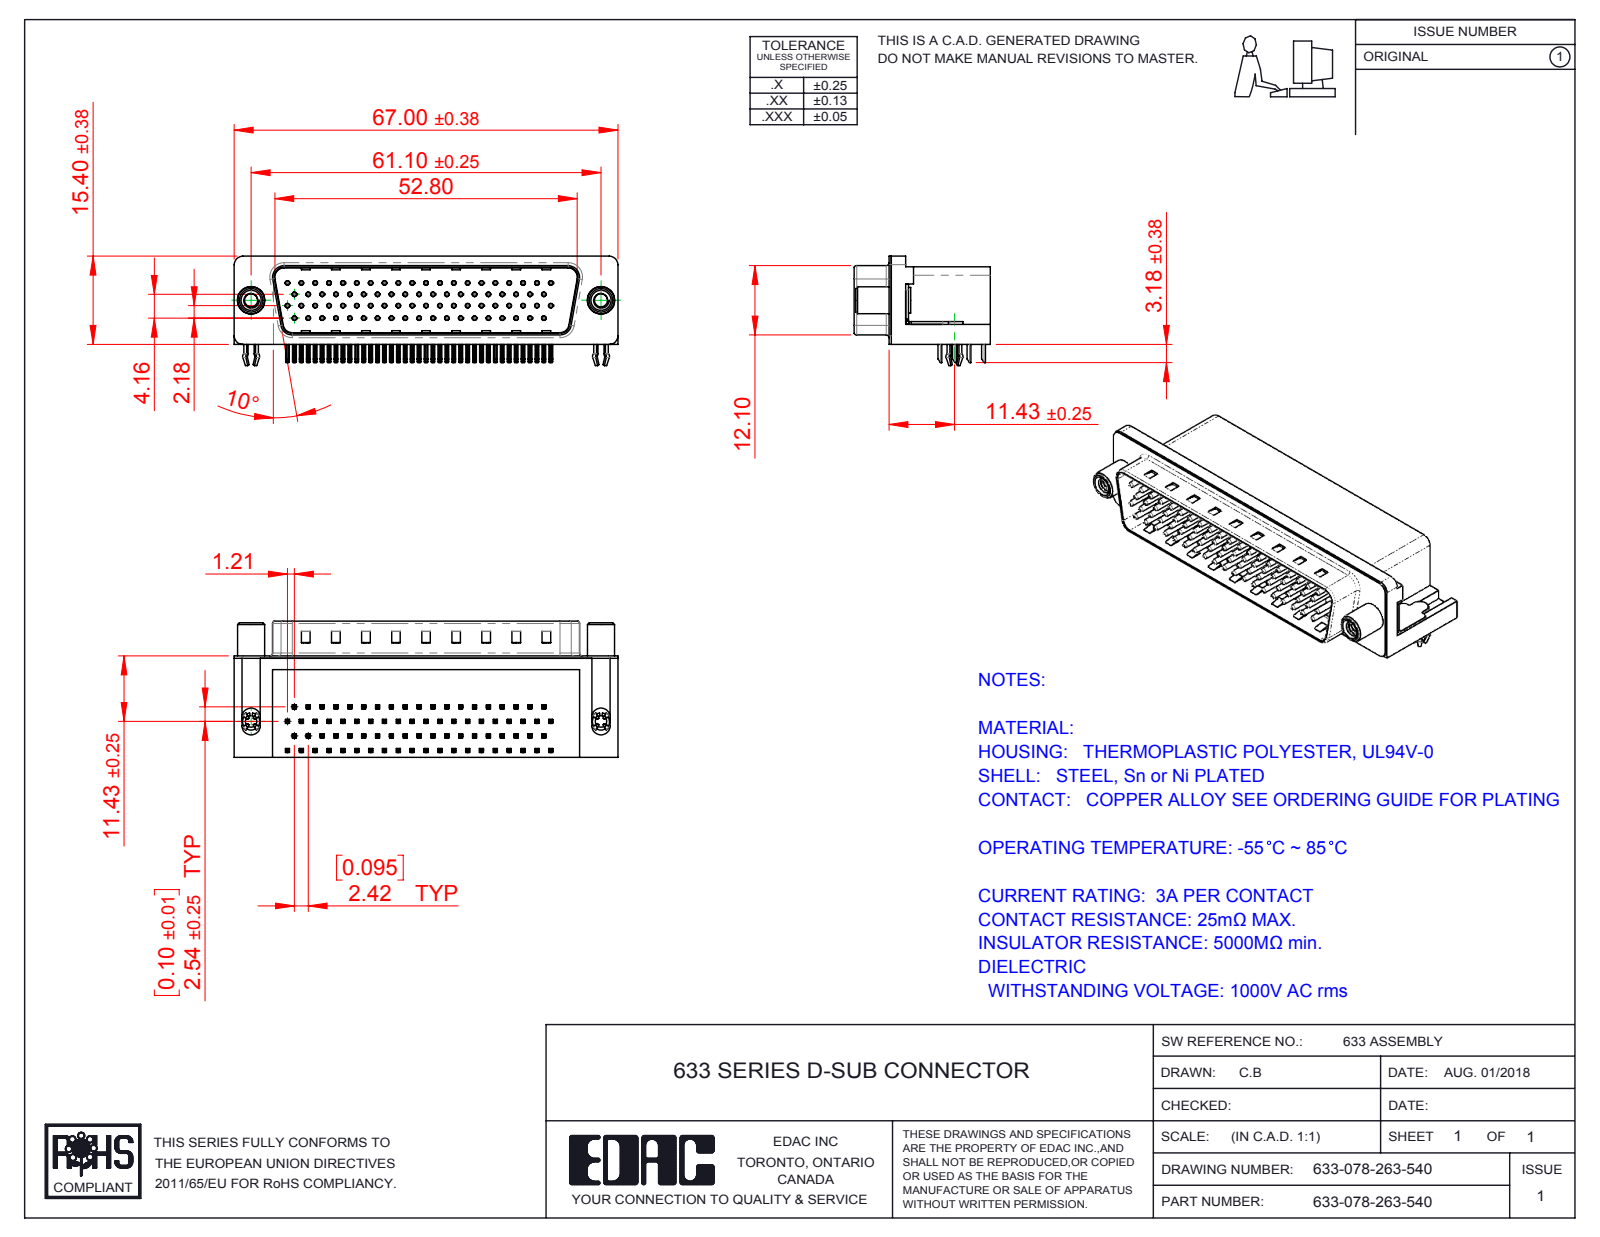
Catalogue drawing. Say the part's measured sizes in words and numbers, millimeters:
The part is named "633 Contact Bottom_78 Contact; 633 Round Threaded Standoff; 633-078-263-540; 633 Contact Top_78 Contact (+5 more)". Its 3-D file was written by "SolidWorks 2016 (CONFIG_CONTROL_DESIGN)". It is 84 solids with 6390 faces: 4015 planar, 1792 cylindrical and 583 other. Overall it measures 67 by 23.8 by 19.1 millimeters. Its volume is 14 713 cubic millimeters and its surface area 16 628 square millimeters. Round holes: 78 of diameter 0.35, 78 of diameter 0.8, 2 of diameter 2, 2 of diameter 2.3, 2 of diameter 3.1, 2 of diameter 4, 2 of diameter 4.8, 2 of diameter 5. Round bosses or shafts: 78 of diameter 0.75, 2 of diameter 4.9, 2 of diameter 4.7, 2 of diameter 4.5, 2 of diameter 3.85, 2 of diameter 3. Partial cylindrical surfaces (rounded edges, fillets, slot ends): 316 of radius 0.25, 156 of radius 0.12, 16 of radius 1, 9 of radius 0.5, 8 of radius 1.6, 6 of radius 1.5, 4 of radius 0.45, 4 of radius 0.9. The main face-to-face distances are 0.4, 13.2, 17.3, 11.7, 13.35, 2.05, 13.75, 1.65, 1.85, 11.9. The hole center spacings are 2.42, 4.84, 7.26, 9.68, 6.26, 7.13, 12.1, 8.62.
